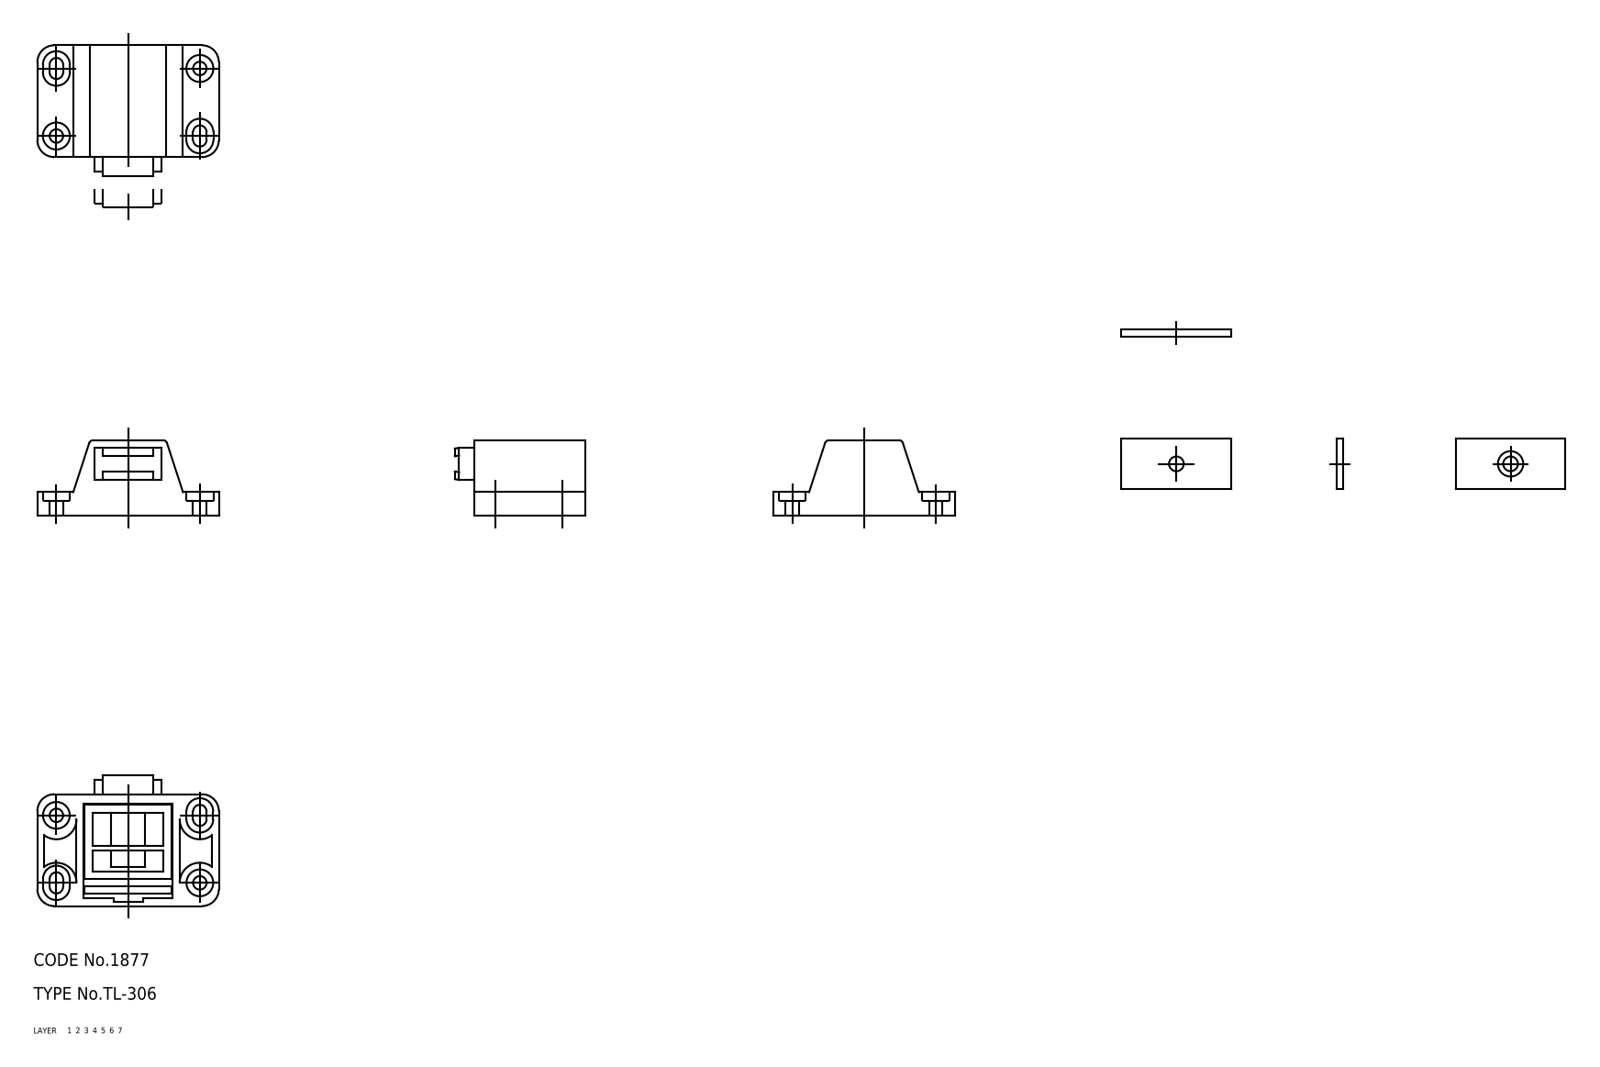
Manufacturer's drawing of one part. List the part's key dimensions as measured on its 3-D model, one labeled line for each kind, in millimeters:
Part name (STEP PRODUCT): 67114311; 67114324; 67114337; 67114350 (+2 more)
STEP written by: CADfix (AUTOMOTIVE_DESIGN)
Units: millimetres
Bodies: 6 solids, 138 faces (0 planar, 0 cylindrical, 138 other)
Overall size (bounding box): 47.02 × 43 × 18.2
Volume: 12 680 mm³ · Surface area: 11 608 mm²
